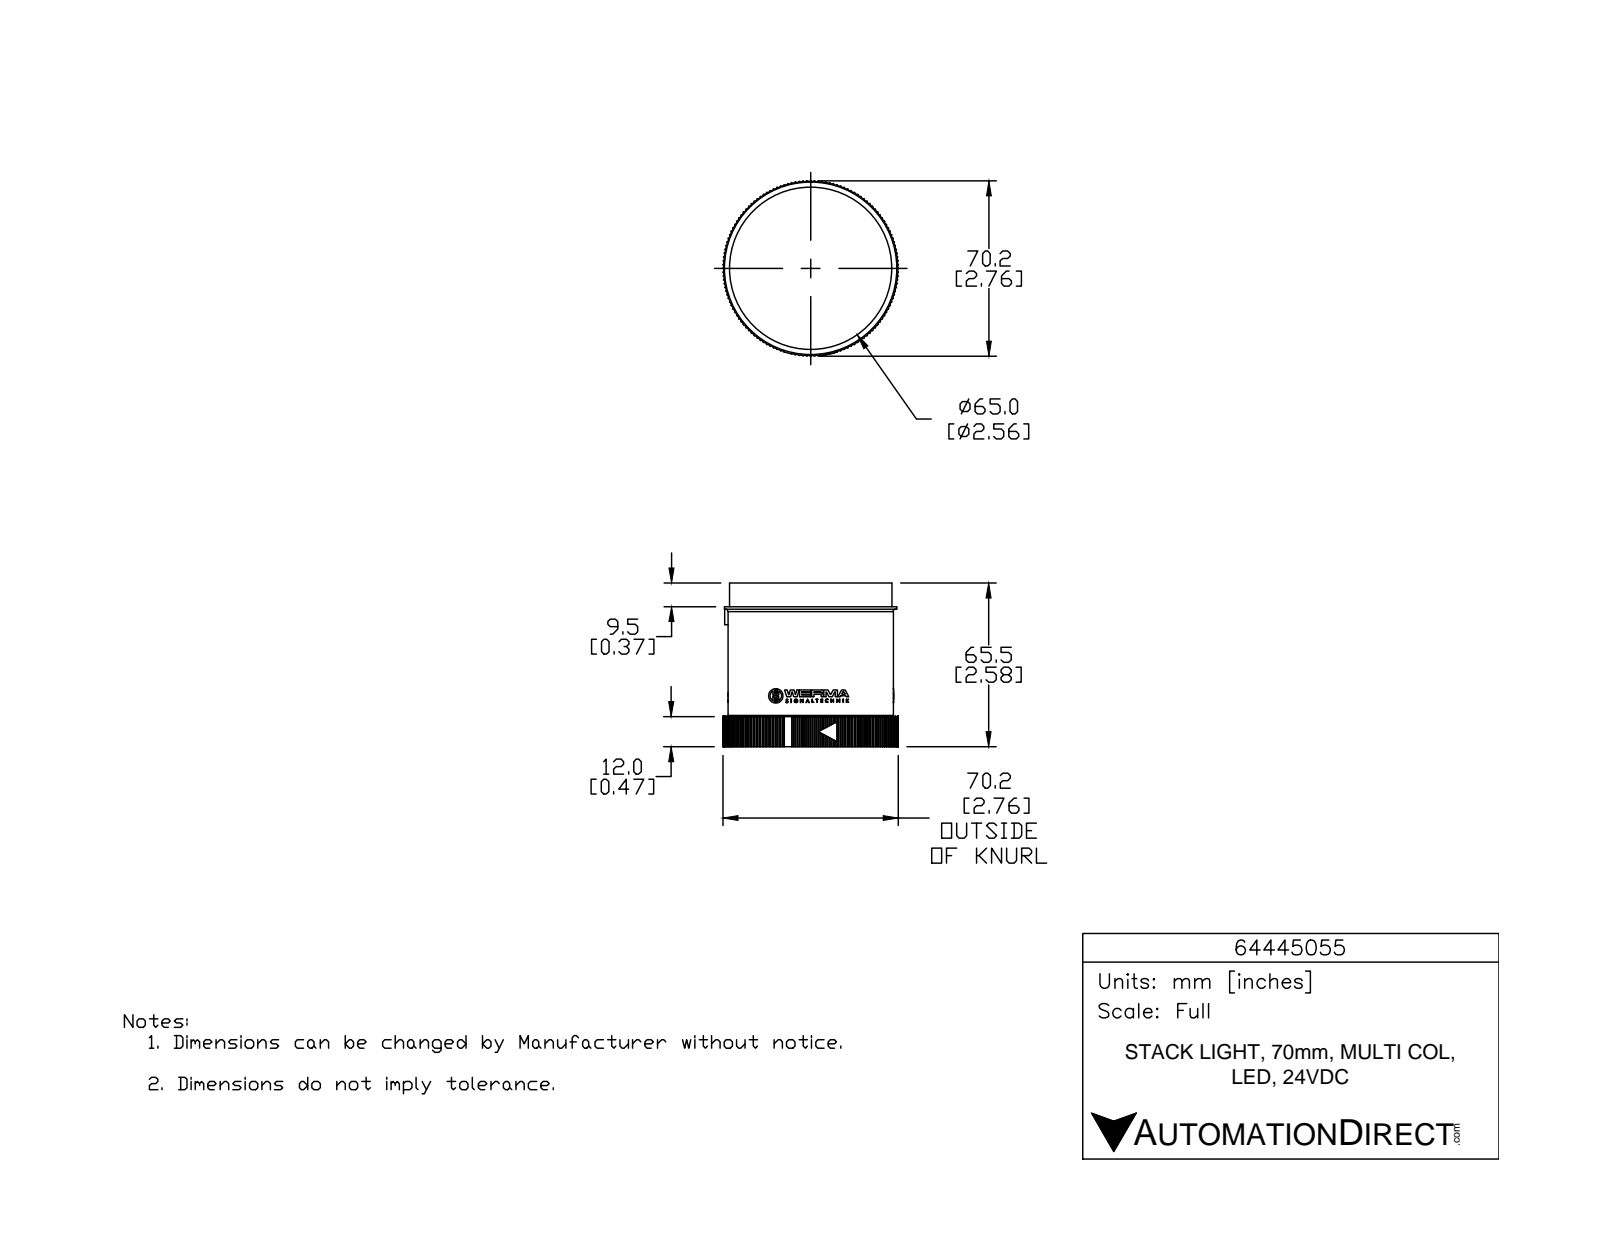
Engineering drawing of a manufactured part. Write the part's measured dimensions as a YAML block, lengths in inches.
part_name: "64445055"
step_written_by: "SolidWorks 2017 (AUTOMOTIVE_DESIGN)"
units: inches
bodies: {solids: 1, faces: 1400, planar: 832, cylindrical: 563, other: 5}
overall_size: [2.762, 2.762, 2.579]
volume: 12.02
surface_area: 37.49
round_holes:
  - {diameter: 0.039, count: 3}
  - {diameter: 2.575, count: 1}
round_bosses_or_shafts:
  - {diameter: 0.226, count: 3}
  - {diameter: 0.056, count: 3}
  - {diameter: 2.717, count: 1}
  - {diameter: 2.606, count: 1}
  - {diameter: 2.559, count: 1}
partial_cylinders:
  - {radius: 0.008, count: 285}
  - {radius: 0.008, count: 6}
  - {radius: 0.008, count: 6}
  - {radius: 0.008, count: 6}
  - {radius: 0.131, count: 6}
  - {radius: 0.004, count: 3}
  - {radius: 0.005, count: 3}
  - {radius: 0.008, count: 3}
face_to_face_distances: [2.201, 2.451, 0.378, 2.579, 2.205, 1.827, 0.374, 2.452, 0.472, 0.094]
